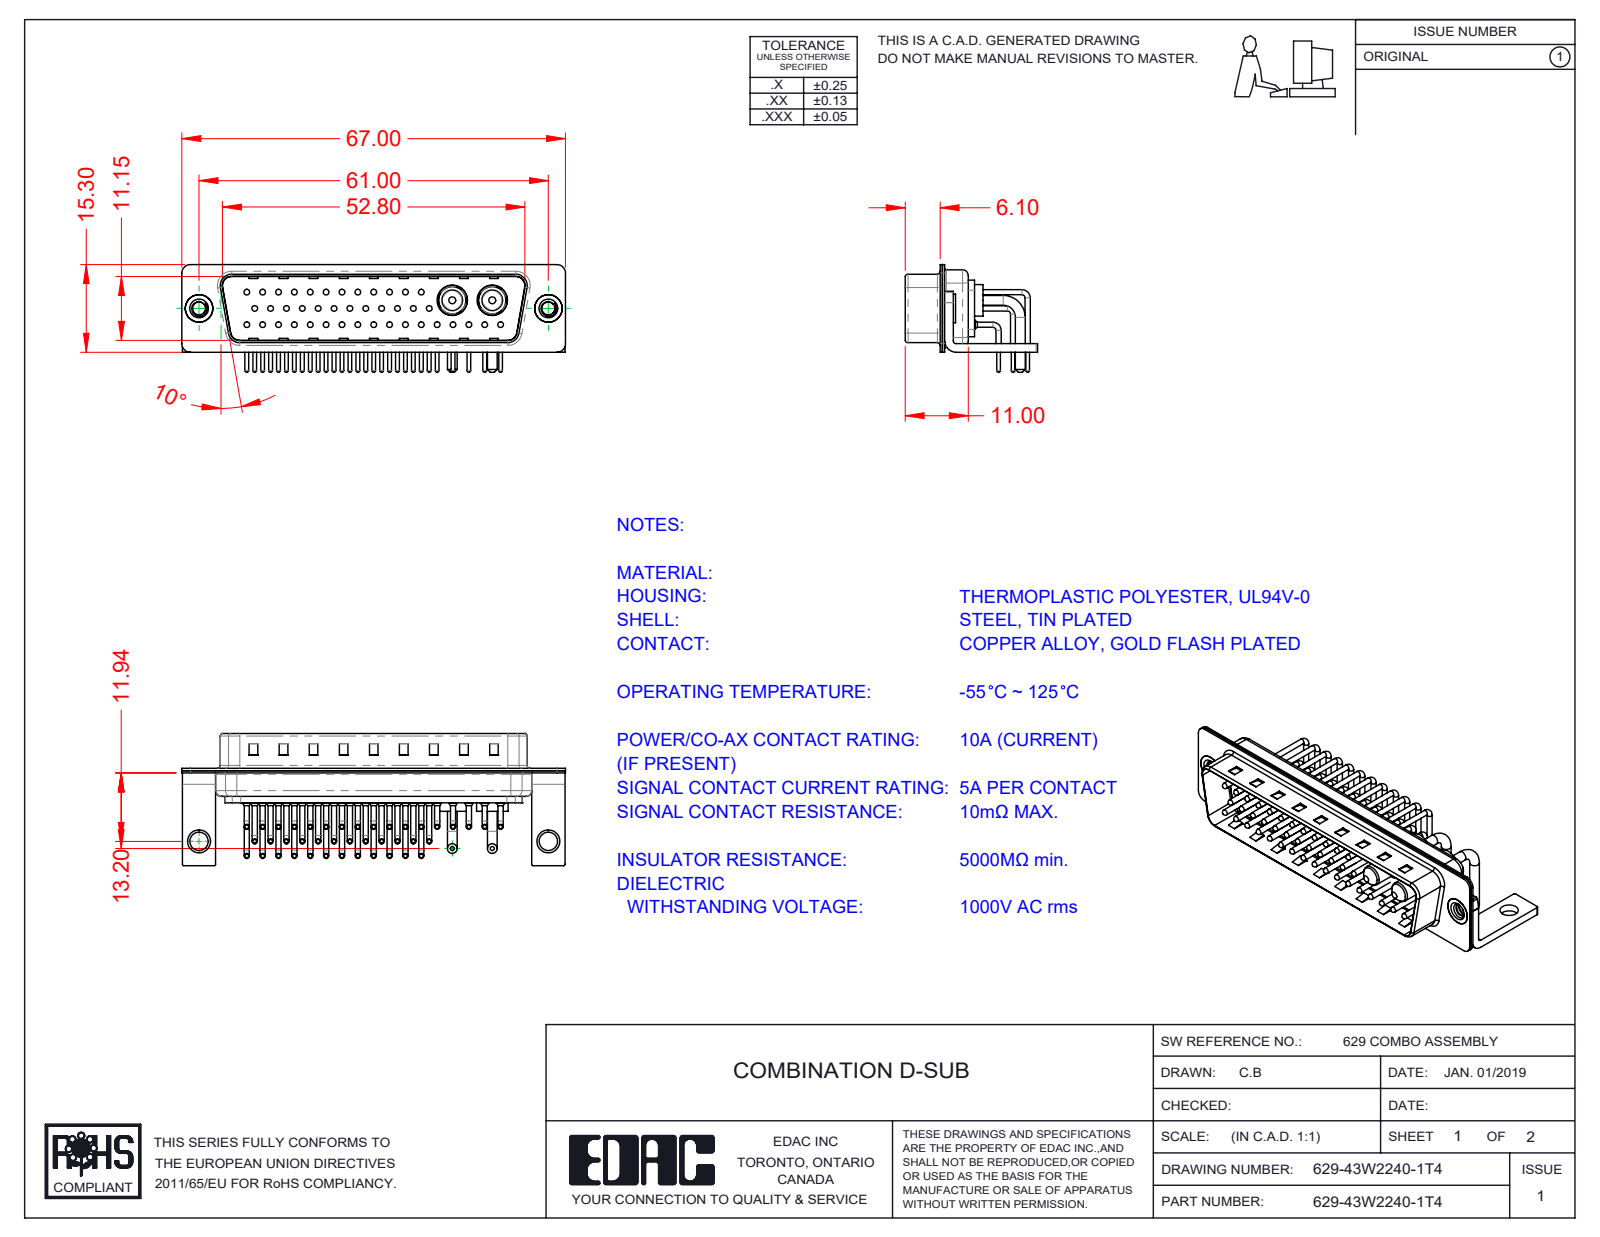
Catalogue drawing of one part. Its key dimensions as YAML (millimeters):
part_name: "629Combo Threaded Rivet_3; 629Combo Shell Rear_50 Contacts; 629Combo Contact Row 3; Power Pin_10A RA 50 (+6 more)"
step_written_by: "SolidWorks 2020 (CONFIG_CONTROL_DESIGN)"
units: millimeters
bodies: {solids: 52, faces: 5048, planar: 2867, cylindrical: 1677, other: 504}
overall_size: [67, 23.1, 18.8]
volume: 5410
surface_area: 13167
round_holes:
  - {diameter: 0.75, count: 41}
  - {diameter: 1.6, count: 41}
  - {diameter: 2, count: 41}
  - {diameter: 2.26, count: 2}
  - {diameter: 3.2, count: 2}
  - {diameter: 4, count: 2}
  - {diameter: 4.8, count: 2}
  - {diameter: 4.85, count: 2}
  - {diameter: 5.3, count: 2}
round_bosses_or_shafts:
  - {diameter: 0.9, count: 82}
  - {diameter: 1.5, count: 41}
  - {diameter: 1, count: 41}
  - {diameter: 0.65, count: 41}
  - {diameter: 1.7, count: 4}
  - {diameter: 5.5, count: 2}
  - {diameter: 5.2, count: 2}
  - {diameter: 5, count: 2}
partial_cylinders:
  - {radius: 1.01, count: 41}
  - {radius: 0.25, count: 16}
  - {radius: 1.5, count: 16}
  - {radius: 2, count: 13}
  - {radius: 0.5, count: 9}
  - {radius: 1.6, count: 8}
  - {radius: 0.6, count: 4}
  - {radius: 0.65, count: 4}
face_to_face_distances: [0.4, 1.5, 11.55, 5.6, 5.2, 0.8, 1.9, 4.1, 6, 0.78]
hole_center_spacings: [2.77, 5.54, 3.16, 8.31, 11.08, 13.85, 16.62, 19.39]
